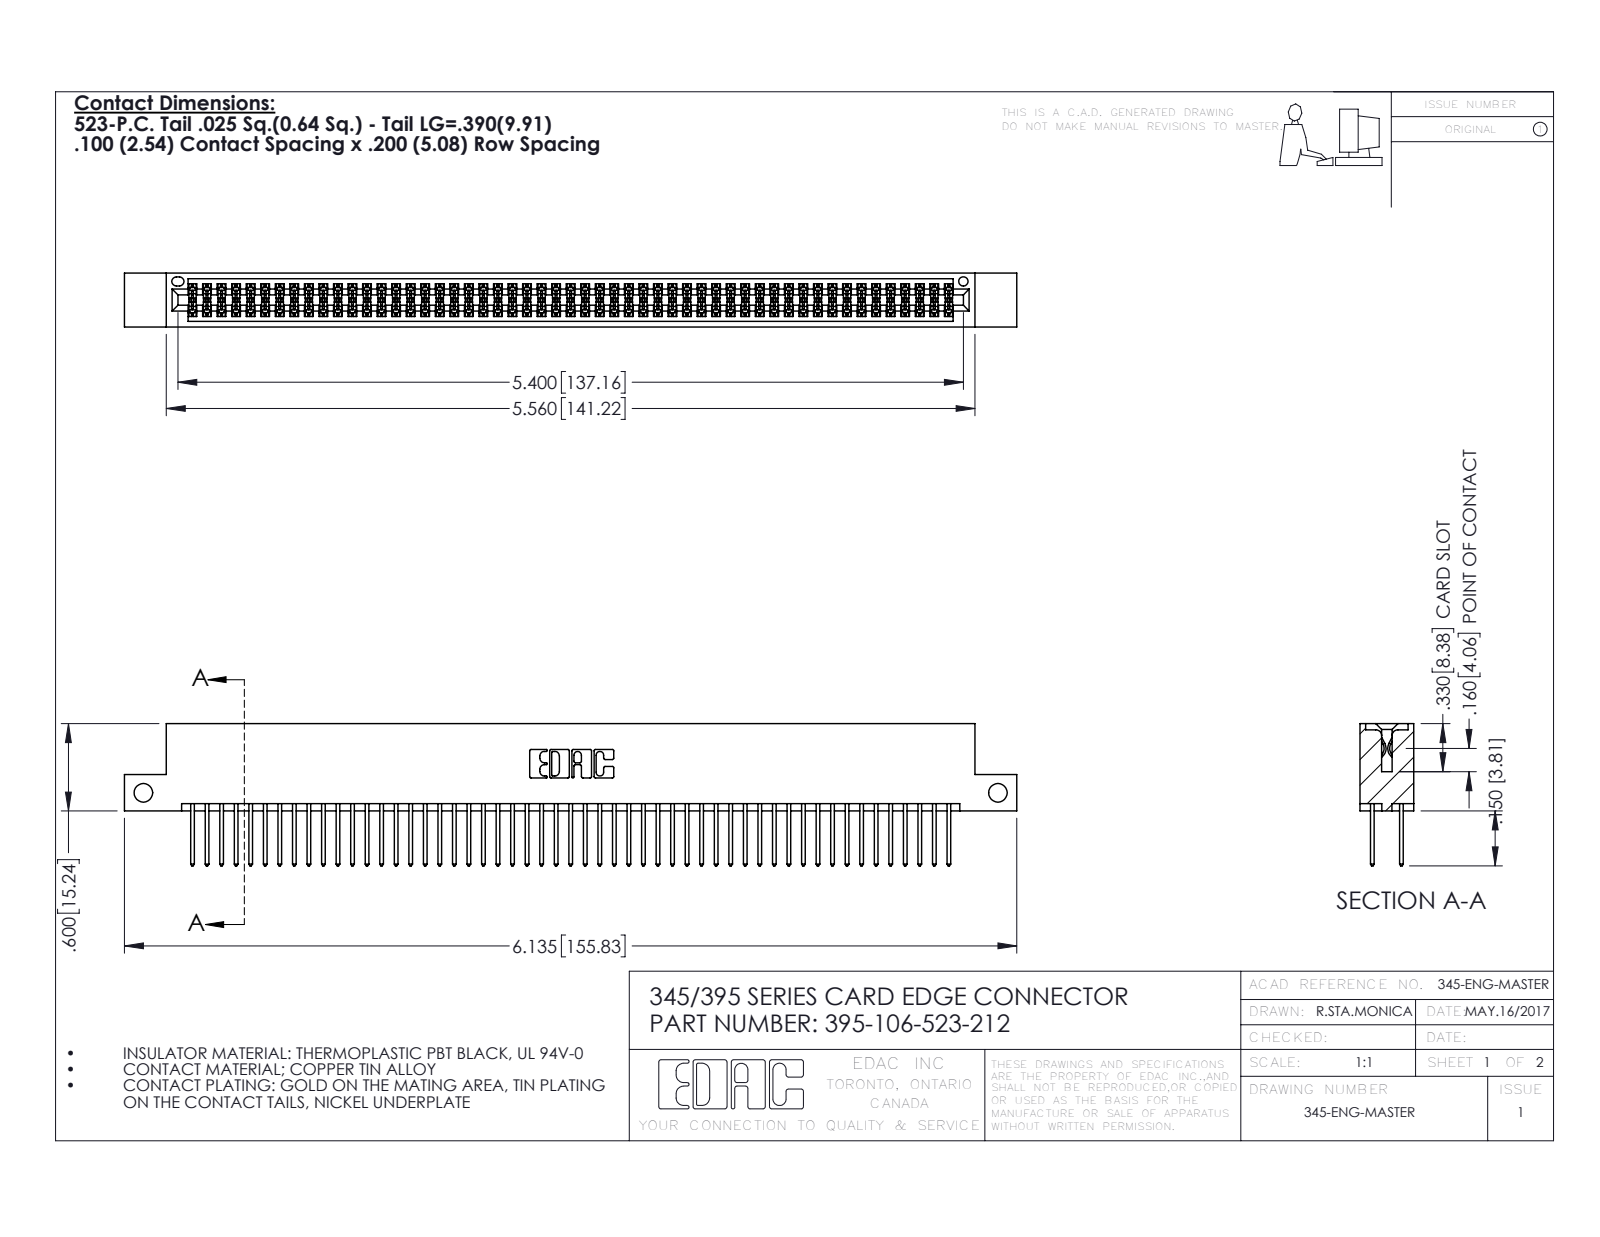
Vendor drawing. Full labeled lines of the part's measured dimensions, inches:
Part name (STEP PRODUCT): 345 Part_Flush Mounting Lugs - Side Mount; 395-106-523-212; 345-292-001_345-293-123
STEP written by: SolidWorks 2016 (CONFIG_CONTROL_DESIGN)
Units: inches
Bodies: 107 solids, 5426 faces (3578 planar, 1848 cylindrical, 0 other)
Overall size (bounding box): 6.135 × 0.977 × 0.37
Volume: 0.938 in³ · Surface area: 36.84 in²
Round holes (diameter × count): ⌀0.128 ×2, ⌀0.064 ×1
Partial cylindrical surfaces — rounded edges, fillets, slot ends (radius × count): R0.006 ×159, R0.01 ×106, R0.01 ×22, R0.007 ×6, R0.031 ×6, R0.026 ×3, R0.014 ×2, R0.019 ×2
Main face-to-face distances: 0.298, 0.072, 0.2, 0.098, 0.272, 0.025, 0.37, 0.225, 0.175, 0.149
Hole centre spacings: 5.875
